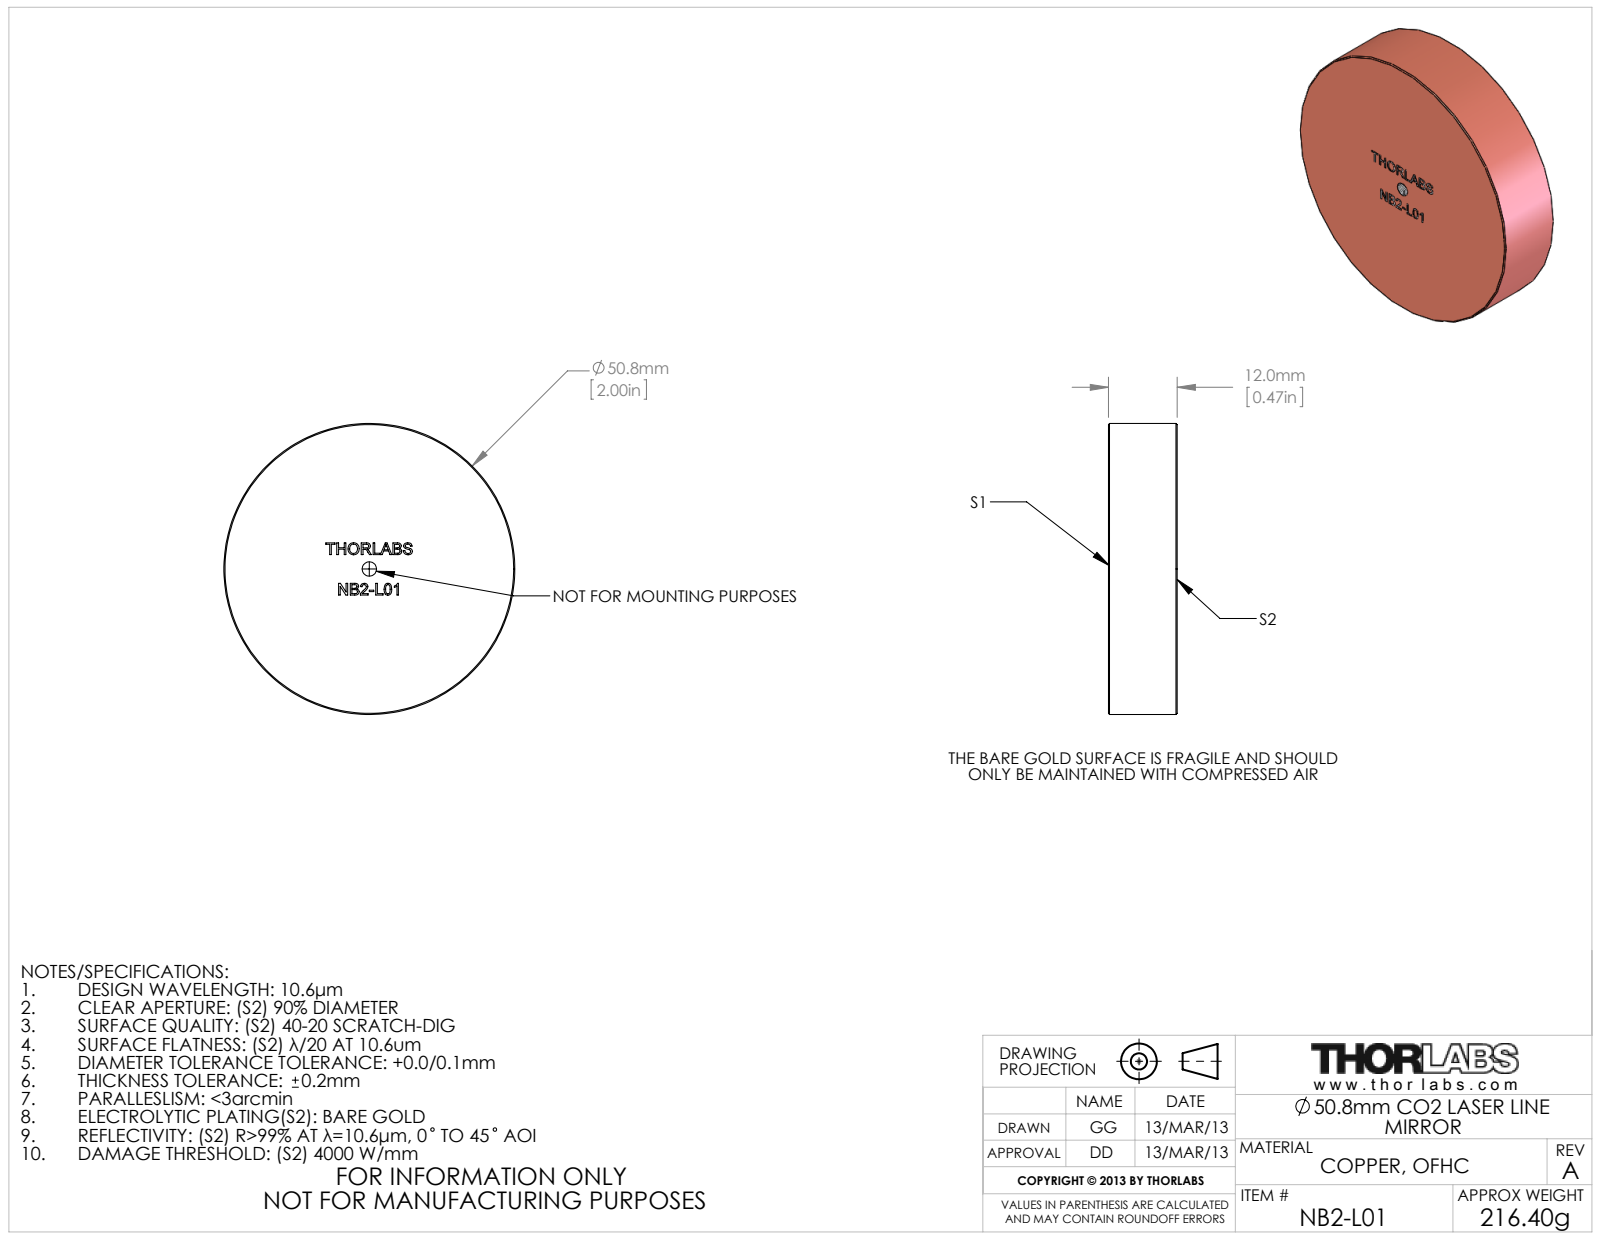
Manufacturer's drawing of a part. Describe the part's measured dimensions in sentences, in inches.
The part is named "24655-E0W". Its 3-D file was written by "SolidWorks 2012 (CONFIG_CONTROL_DESIGN)". It is 0 solids with 33 faces: 25 planar, 4 cylindrical and 4 other. Overall it measures 2 by 2 by 0.472 inches. Round holes: 1 of diameter 0.098. Round bosses or shafts: 1 of diameter 2. The main face-to-face distances are 0.472.
